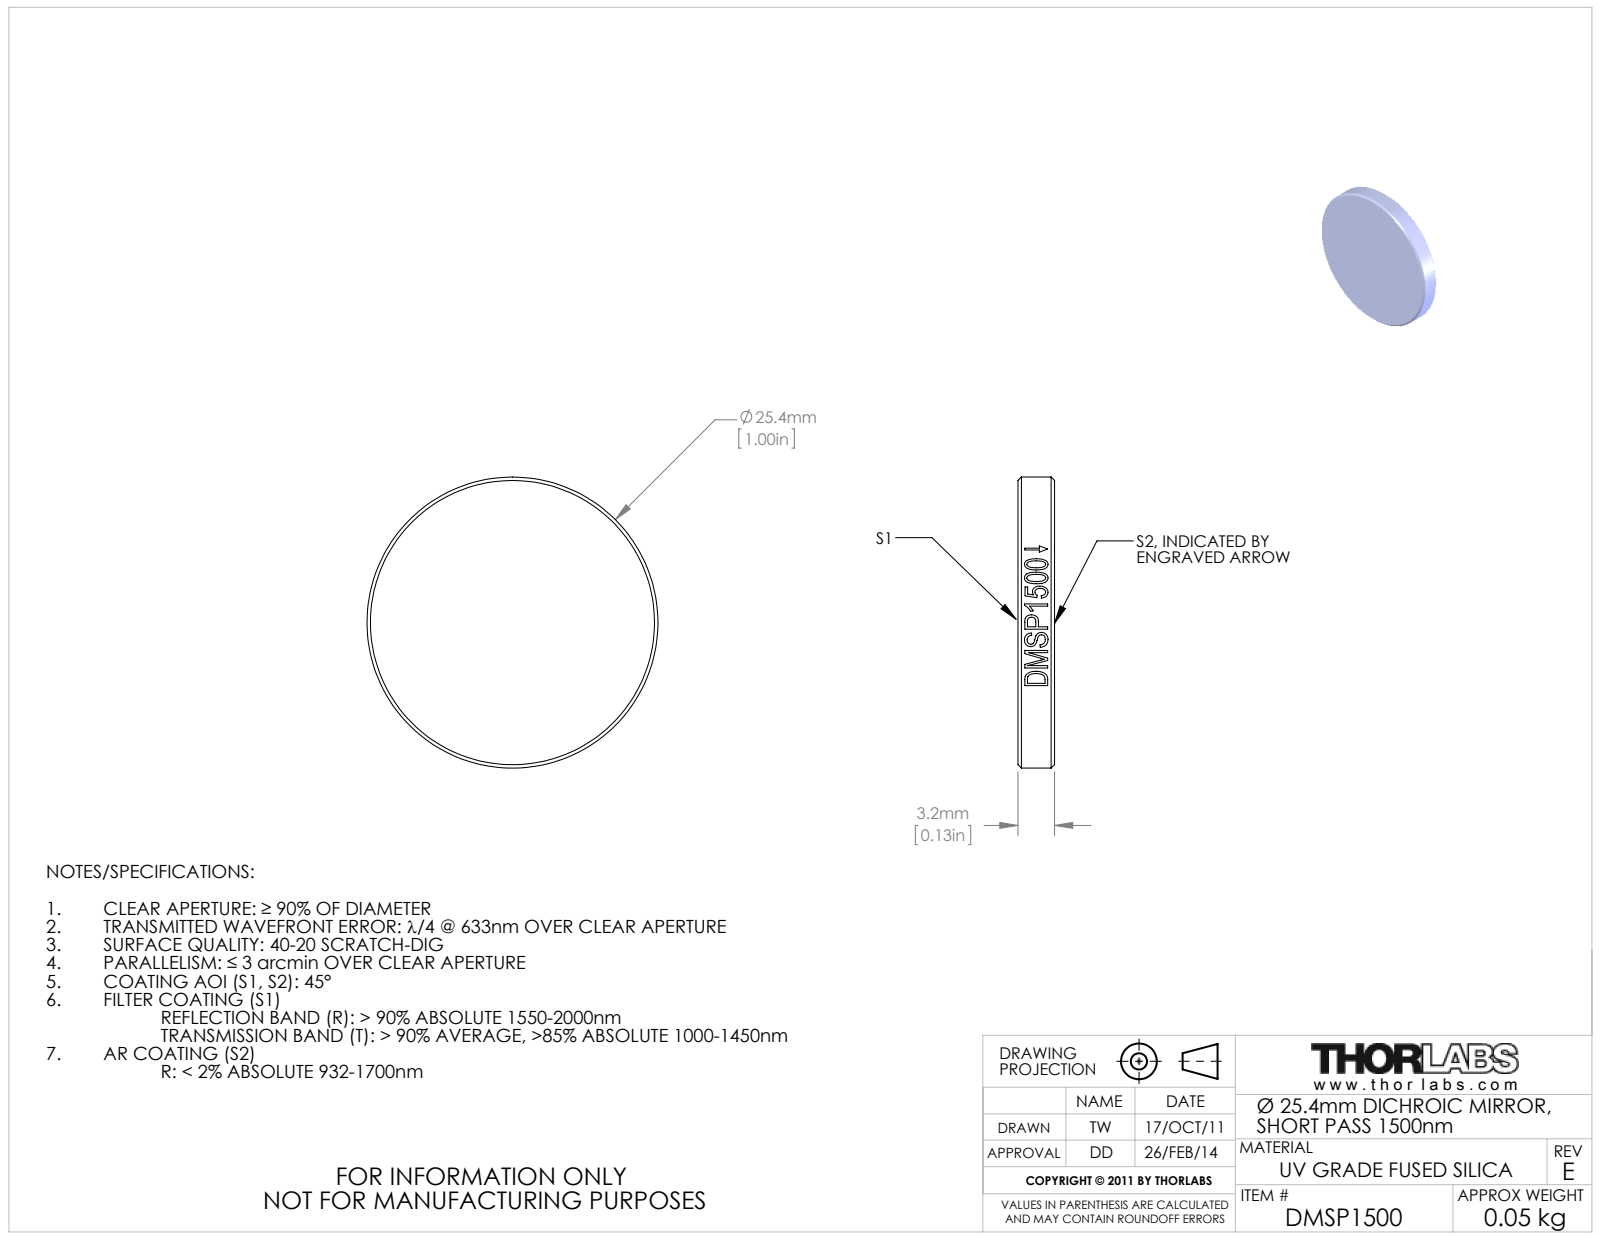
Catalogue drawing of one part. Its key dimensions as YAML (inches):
part_name: "21941-E0W"
step_written_by: "SolidWorks 2011 (CONFIG_CONTROL_DESIGN)"
units: inches
bodies: {solids: 0, faces: 21, planar: 2, cylindrical: 15, other: 4}
overall_size: [1, 1, 0.126]
round_bosses_or_shafts:
  - {diameter: 1, count: 1}
face_to_face_distances: [0.126]
